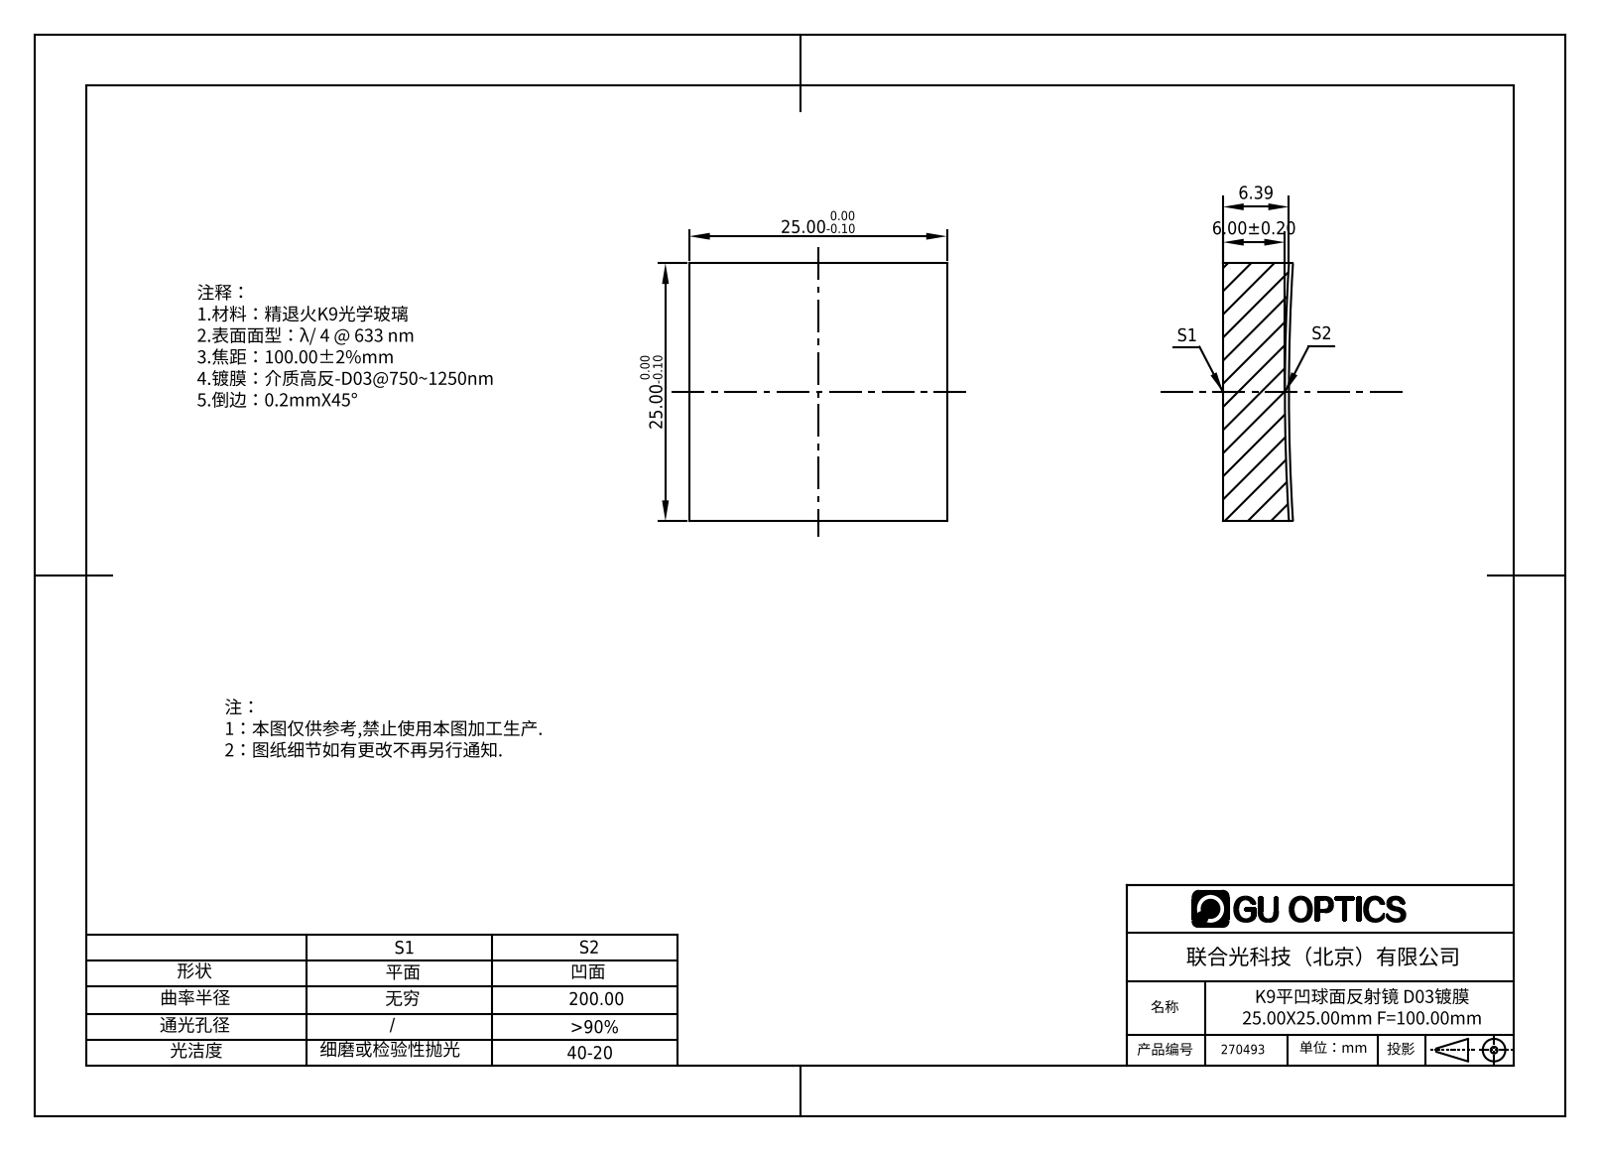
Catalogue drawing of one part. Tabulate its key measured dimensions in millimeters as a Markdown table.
| quantity | value |
| --- | --- |
| part name | 270038 |
| STEP written by | SolidWorks 2019 (AUTOMOTIVE_DESIGN) |
| units | millimeters |
| bodies | 1 solid, 7 faces (5 planar, 0 cylindrical, 2 other) |
| overall size | 25 × 25 × 6.78 |
| volume | 3 913 mm³ |
| surface area | 1 903 mm² |
| main face-to-face distances | 25 |
